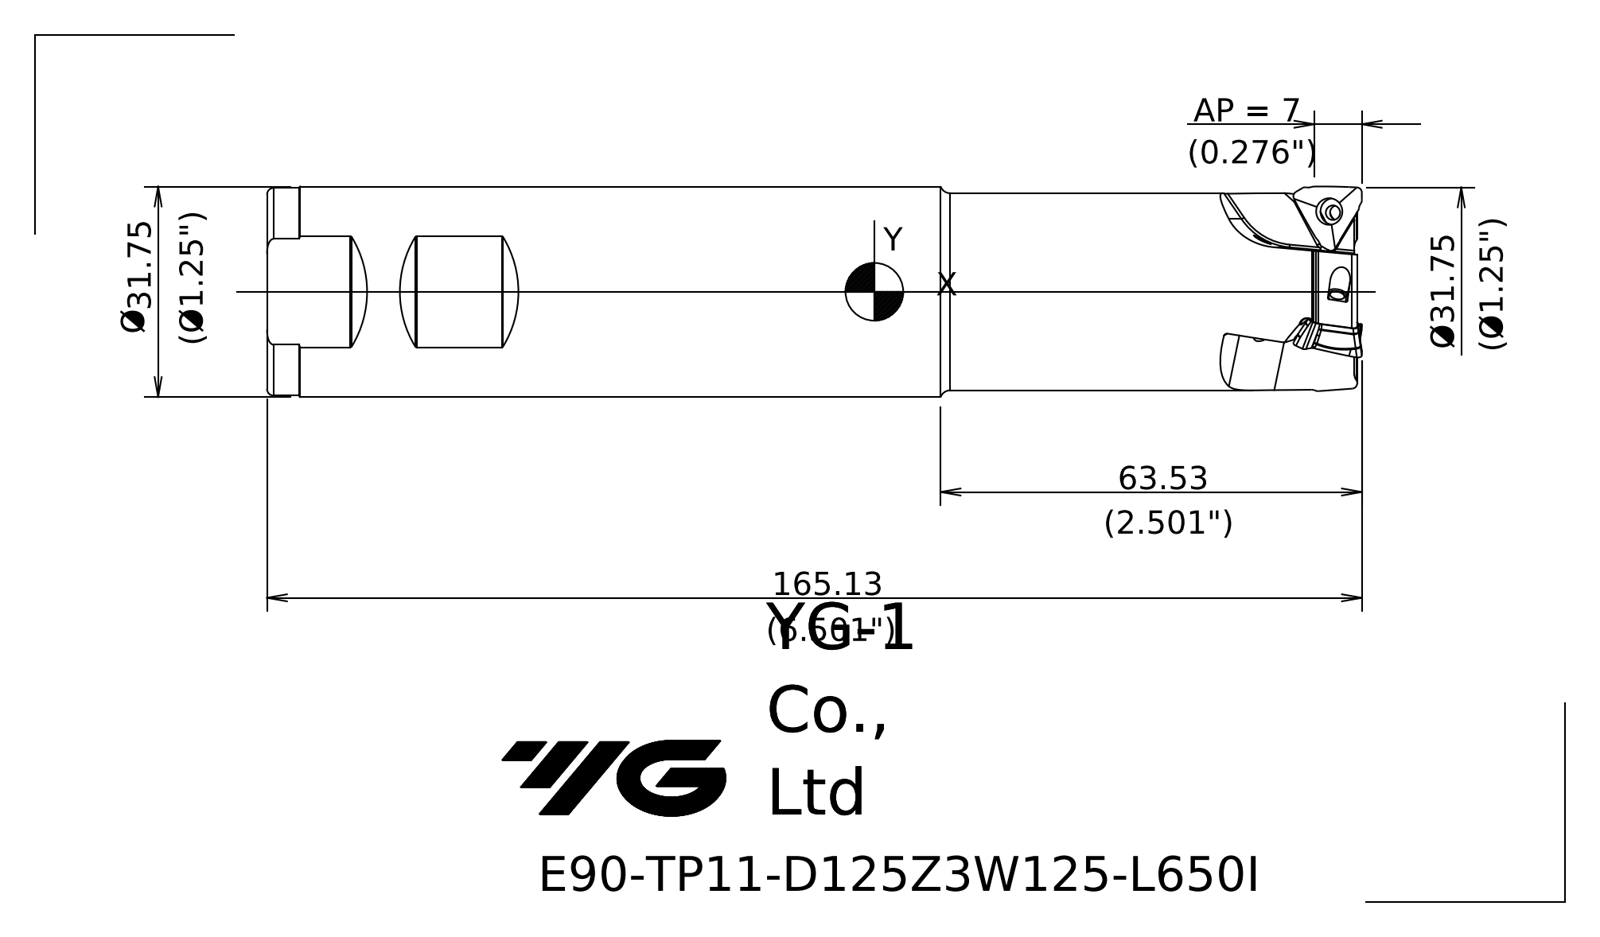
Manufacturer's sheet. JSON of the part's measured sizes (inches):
{"part_name": "10222DA0A397nvi5", "step_written_by": "SIEMENS PLM Software NX 10.0 (AP203_CONFIGURATION_CONTROLLED_3D_DESIGN_OF_MECHANICAL_PARTS_AND_ASSEMBLIES_MIM_LF)", "units": "inches", "bodies": {"solids": 1, "faces": 63, "planar": 8, "cylindrical": 14, "other": 41}, "overall_size": [6.501, 1.253, 1.253], "volume_in3": 7.059, "surface_area_in2": 37.05, "round_holes": [[0.079, 3], [0.094, 3], [0.059, 1], [0.315, 1]], "round_bosses_or_shafts": [[1.25, 1], [1.234, 1], [1.171, 1]], "partial_cylinders_radius": [[0.012, 3]], "face_to_face_distances": [6.457, 0.635, 0.016, 6.472]}
